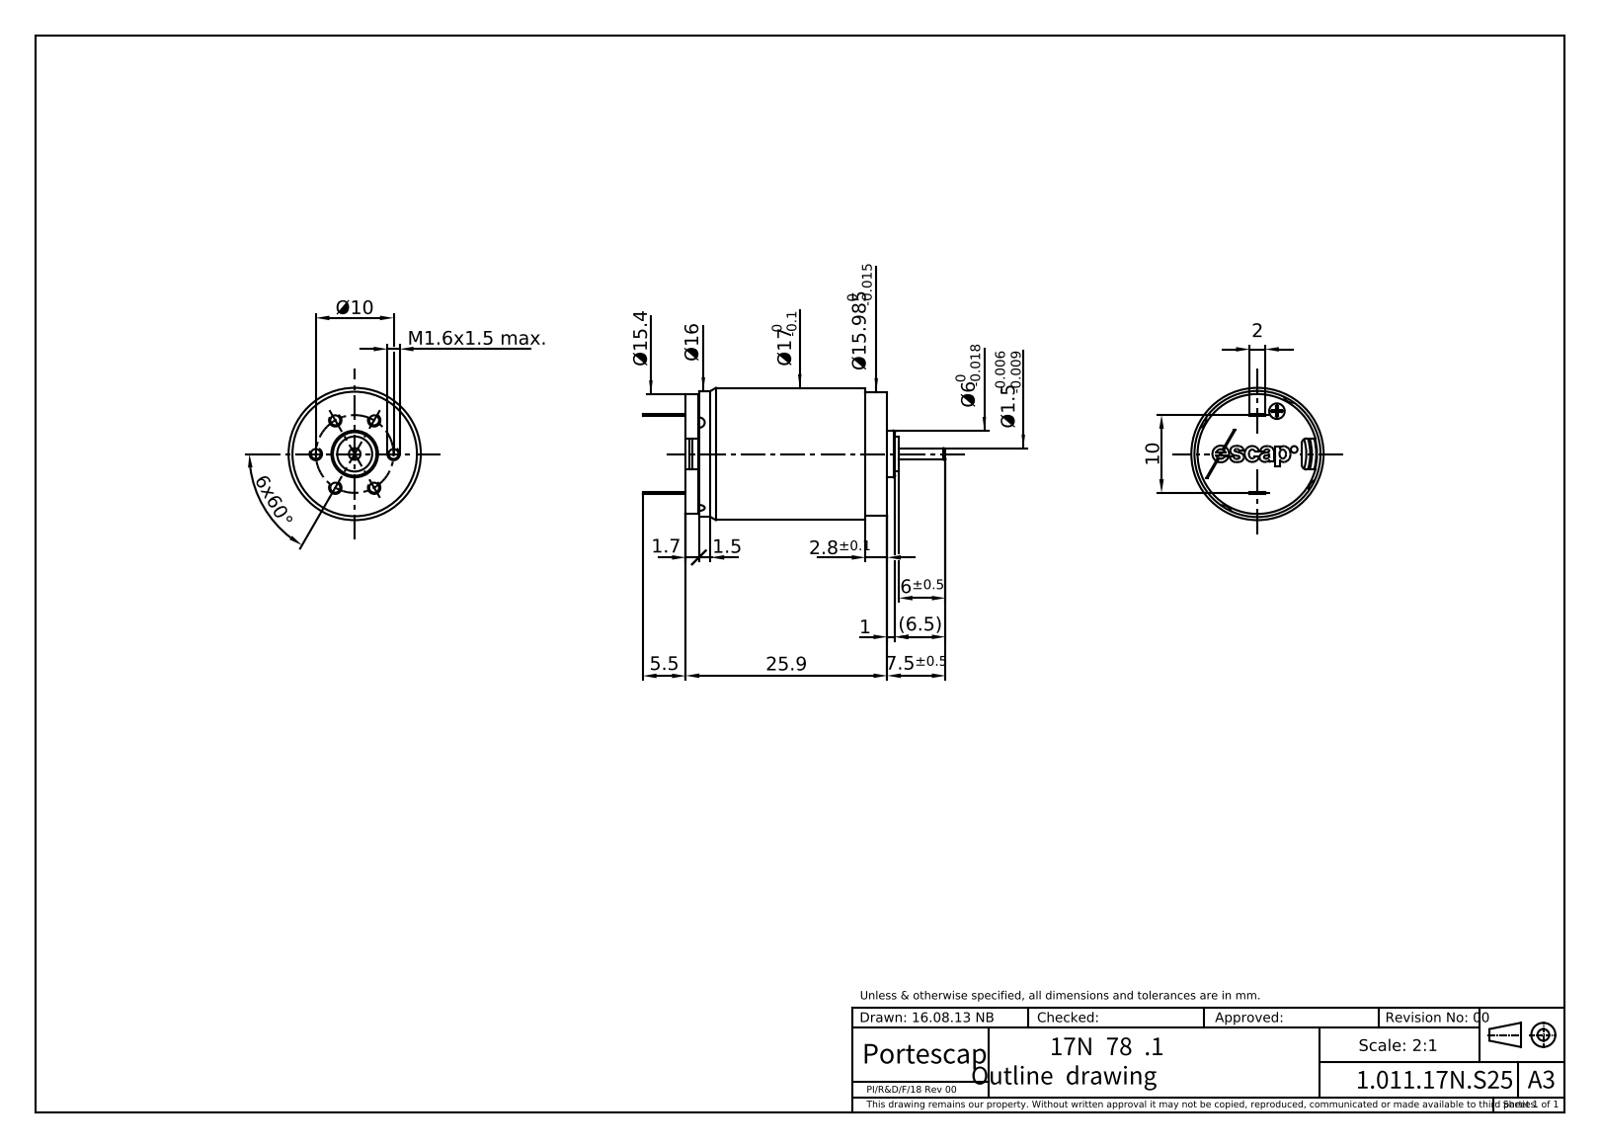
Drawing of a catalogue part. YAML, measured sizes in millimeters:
part_name: "17N78_210E_1"
step_written_by: "PRO/ENGINEER BY PARAMETRIC TECHNOLOGY CORPORATION, 2014310 (CONFIG_CONTROL_DESIGN)"
units: millimeters
bodies: {solids: 2, faces: 381, planar: 311, cylindrical: 46, other: 24}
overall_size: [38.9, 17, 17]
volume: 5719
surface_area: 1990
round_holes:
  - {diameter: 1.25, count: 6}
  - {diameter: 0.6, count: 1}
  - {diameter: 2, count: 1}
round_bosses_or_shafts:
  - {diameter: 17, count: 1}
  - {diameter: 16, count: 1}
  - {diameter: 15.98, count: 1}
  - {diameter: 15.4, count: 1}
  - {diameter: 15.3, count: 1}
  - {diameter: 6, count: 1}
  - {diameter: 5.5, count: 1}
  - {diameter: 1.5, count: 1}
partial_cylinders:
  - {radius: 0.1, count: 2}
  - {radius: 0.2, count: 2}
  - {radius: 0.5, count: 2}
  - {radius: 0.6, count: 2}
  - {radius: 6.3, count: 1}
face_to_face_distances: [25.9, 1.7, 2.8, 23.1, 10, 1.5, 21.4, 24.2, 27.4, 25.7]
hole_center_spacings: [5, 8.66, 10, 0.5, 1.17, 4.57, 5.14, 5.44]
